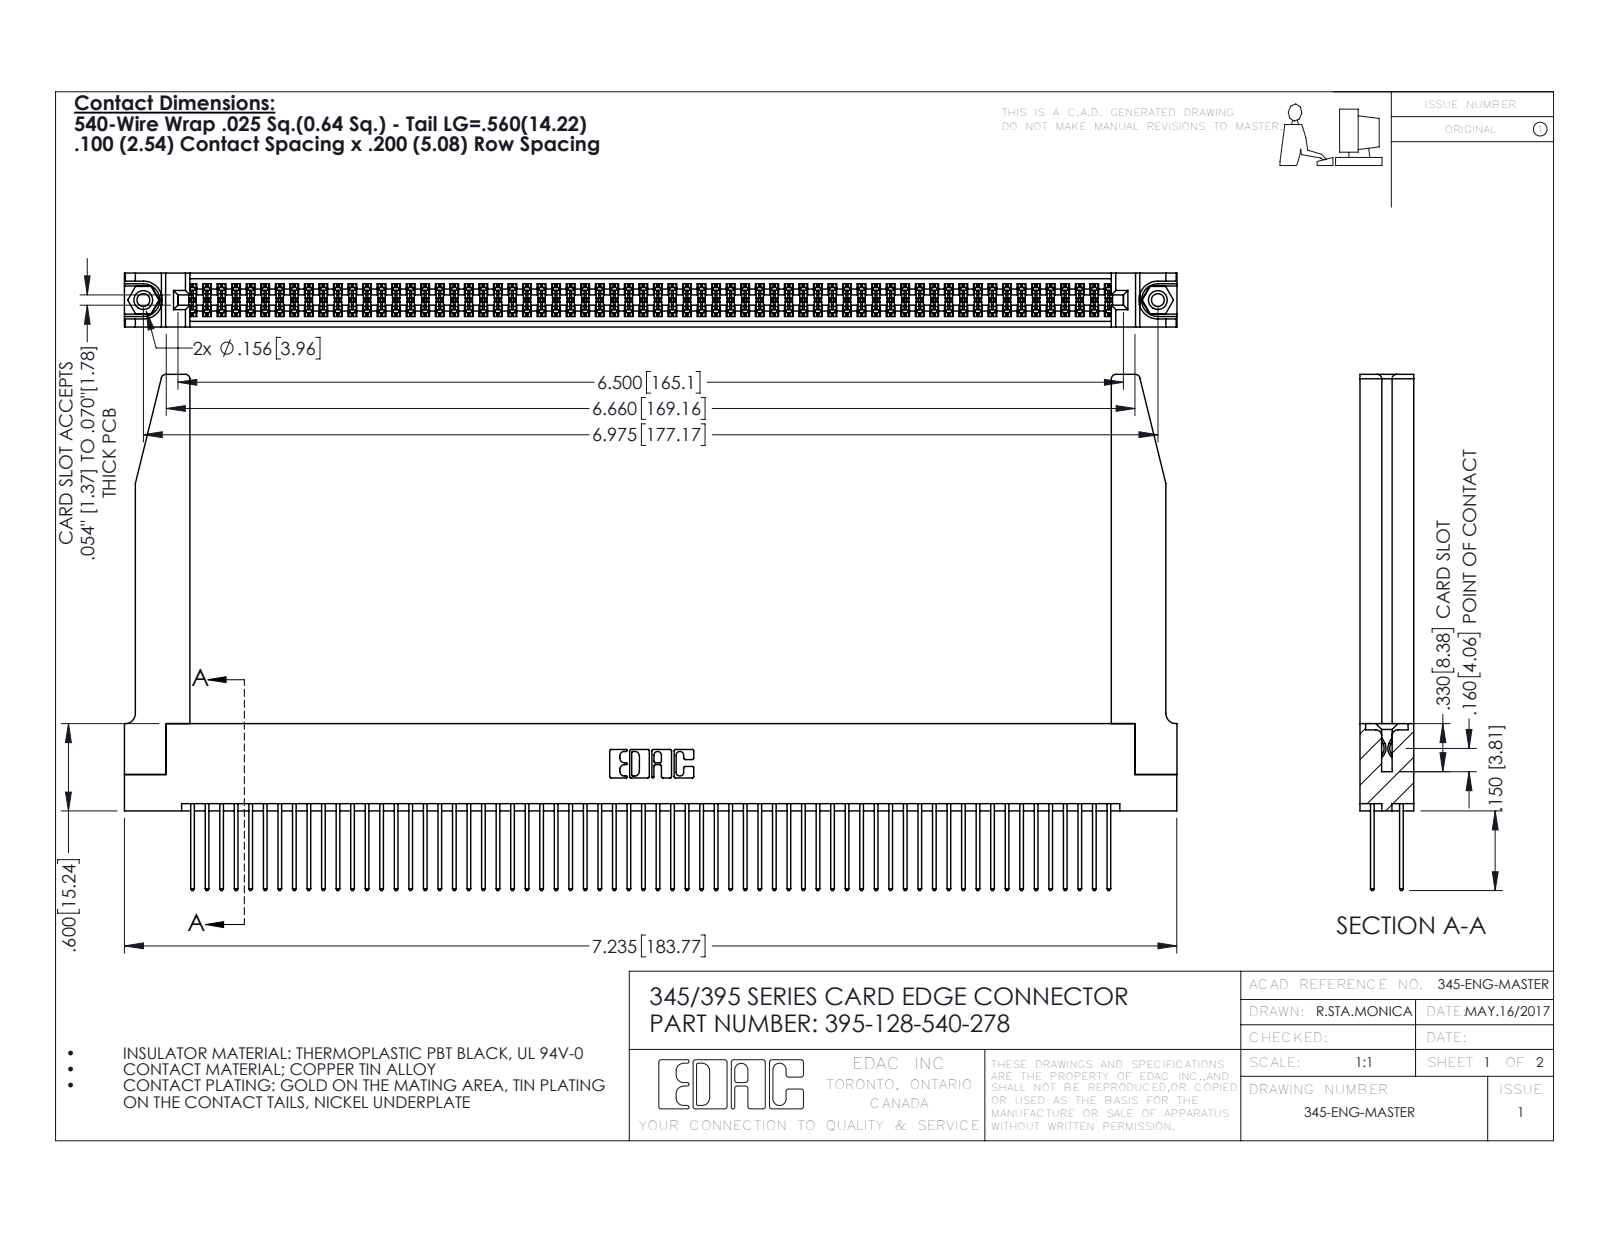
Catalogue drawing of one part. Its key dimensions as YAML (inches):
part_name: "345-250-001_345-250-001-102; 345-292-001_345-293-140; 345-220-078_345-220-078; 345 Part_Flush Mounting Lugs - 0.156 Dia-TH (+1 more)"
step_written_by: "SolidWorks 2016 (CONFIG_CONTROL_DESIGN)"
units: inches
bodies: {solids: 133, faces: 6760, planar: 4446, cylindrical: 2262, other: 52}
overall_size: [7.236, 3.547, 0.37]
volume: 1.606
surface_area: 57.24
round_holes:
  - {diameter: 0.089, count: 2}
  - {diameter: 0.125, count: 2}
  - {diameter: 0.156, count: 2}
  - {diameter: 0.064, count: 1}
round_bosses_or_shafts:
  - {diameter: 0.155, count: 2}
partial_cylinders:
  - {radius: 0.006, count: 192}
  - {radius: 0.01, count: 128}
  - {radius: 0.01, count: 22}
  - {radius: 0.03, count: 8}
  - {radius: 0.007, count: 6}
  - {radius: 0.031, count: 6}
  - {radius: 0.026, count: 3}
  - {radius: 0.014, count: 2}
face_to_face_distances: [0.072, 0.298, 0.37, 0.2, 0.098, 0.272, 0.025, 0.225, 0.175, 0.148]
hole_center_spacings: [0.27, 6.739, 6.975]
